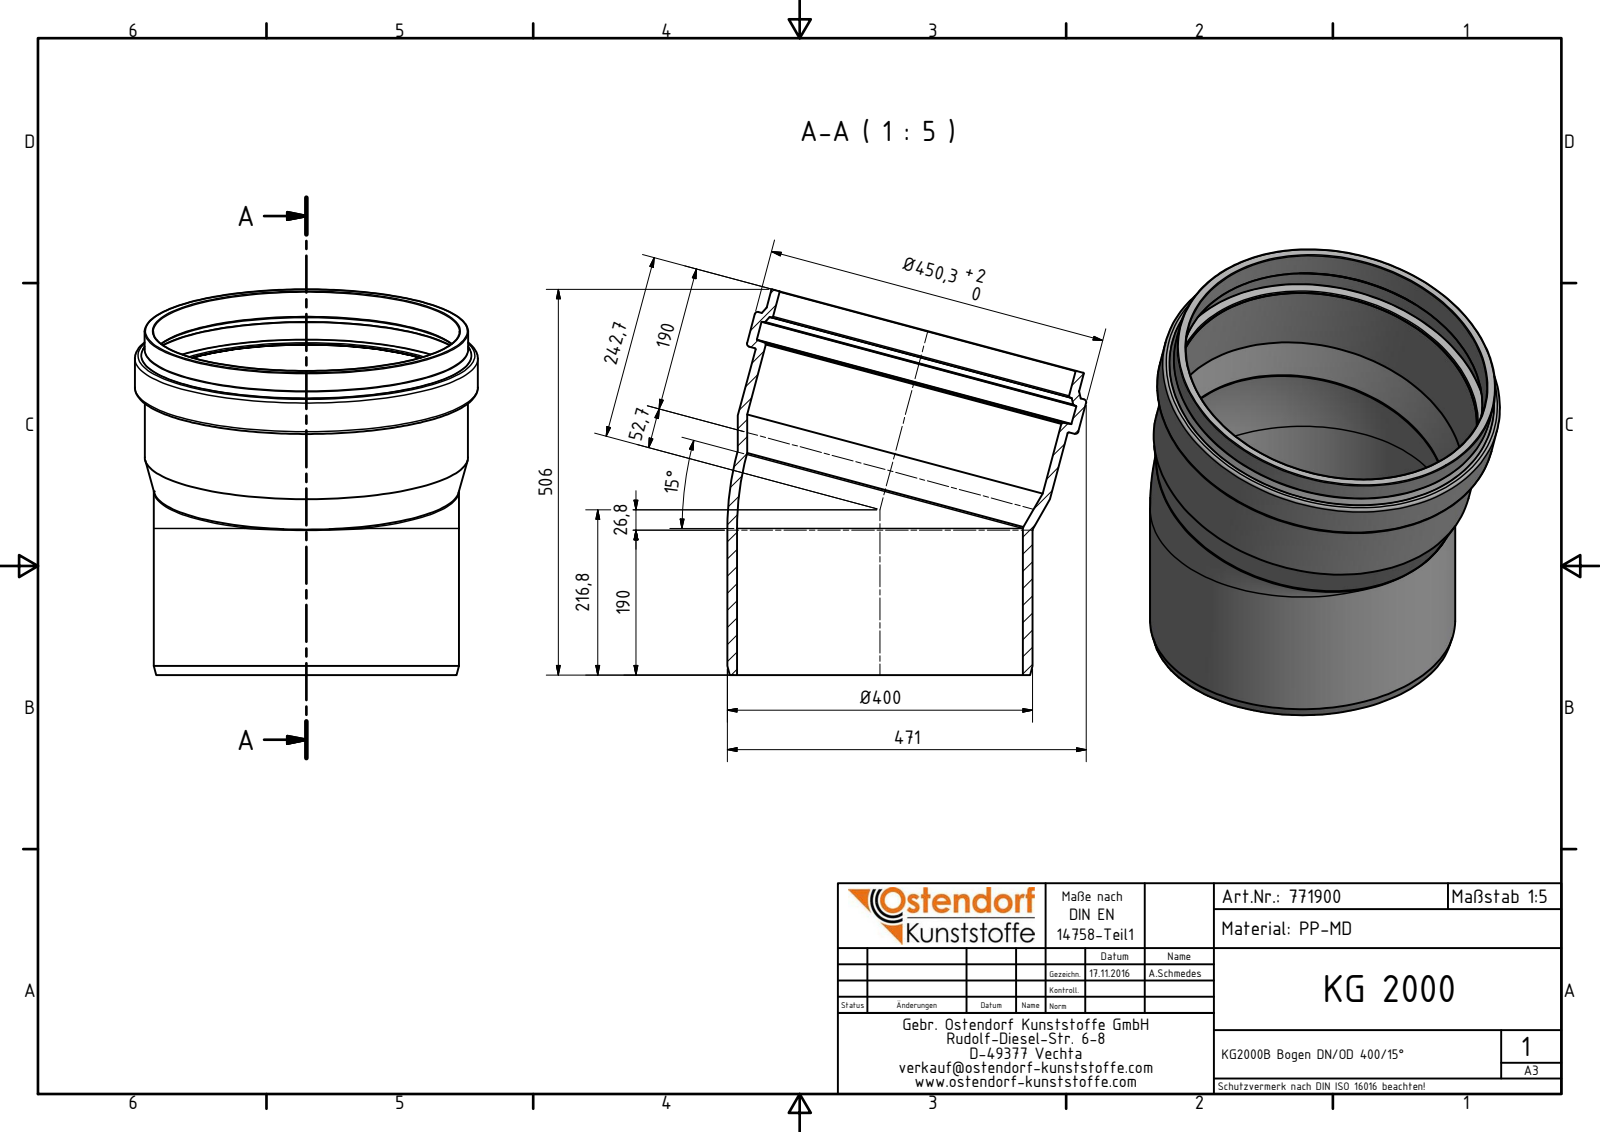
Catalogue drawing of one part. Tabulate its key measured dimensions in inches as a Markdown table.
| quantity | value |
| --- | --- |
| part name | 771900 KG2000B Bogen DN_OD 400_15° |
| STEP written by | Autodesk Inventor 2016 (AUTOMOTIVE_DESIGN) |
| units | inches |
| bodies | 1 solid, 40 faces (5 planar, 11 cylindrical, 24 other) |
| overall size | 19.921 × 18.543 × 17.728 |
| volume | 438.2 in³ |
| surface area | 1 916 in² |
| round holes (diameter × count) | 14.783 × 2, 15.831 × 2, 15.815 × 1, 16.839 × 1 |
| round bosses / shafts (diameter × count) | 15.768 × 2, 17.728 × 1, 16.72 × 1, 16.705 × 1 |
| main face-to-face distances | 3.166, 1.851, 1.315, 0.32, 1.53, 2.845 |
